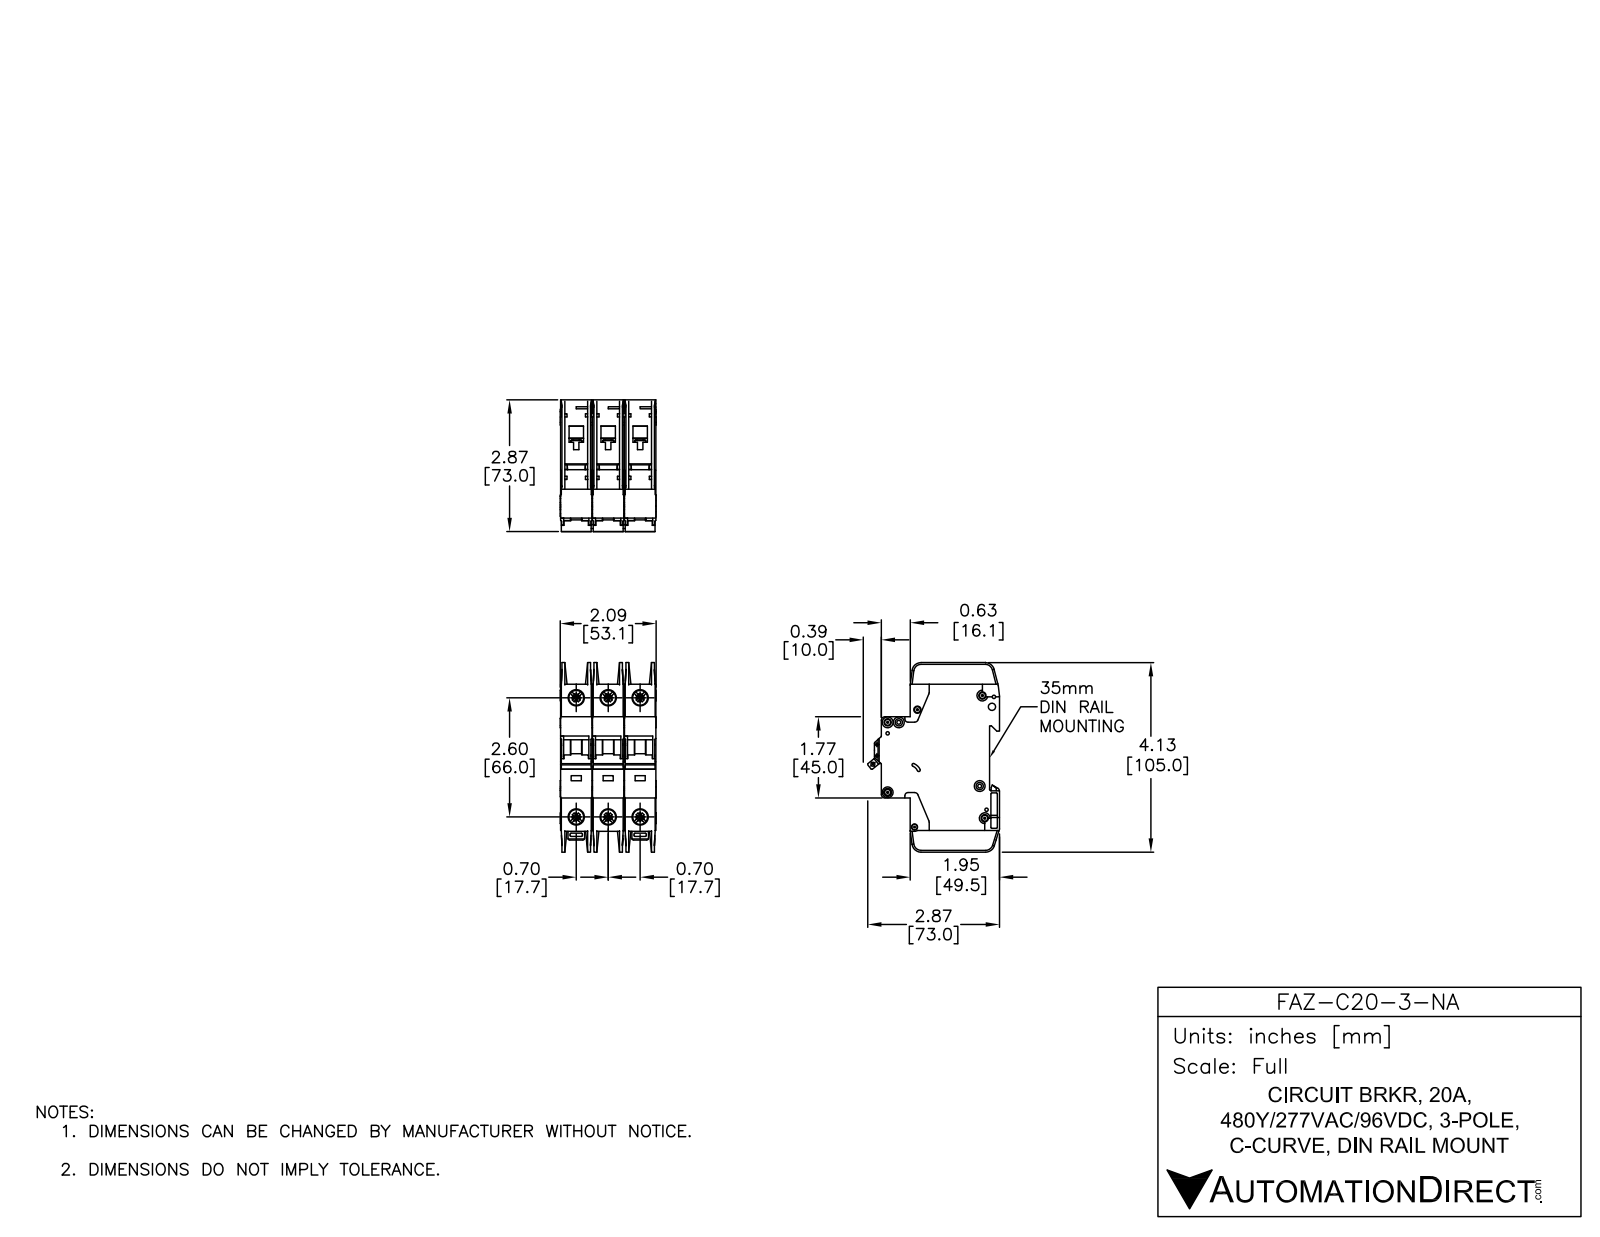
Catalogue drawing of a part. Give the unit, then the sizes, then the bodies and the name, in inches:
Units: inches
Overall size (bounding box): 4.134 × 2.876 × 2.091
Round holes (diameter × count): ⌀0.142 ×7, ⌀0.281 ×6, ⌀0.323 ×6, ⌀0.043 ×2, ⌀0.059 ×2, ⌀0.157 ×2, ⌀0.075 ×1, ⌀0.085 ×1, ⌀0.087 ×1, ⌀0.1 ×1, ⌀0.13 ×1, ⌀0.134 ×1
Round bosses / shafts (diameter × count): ⌀0.236 ×7, ⌀0.098 ×3
Partial cylindrical surfaces — rounded edges, fillets, slot ends (radius × count): R0.01 ×65, R0.02 ×30, R0.039 ×26, R0.079 ×14, R0.071 ×5, R0.197 ×5, R0.157 ×4, R0.008 ×2
Main face-to-face distances: 0.697, 1.394, 0.689, 1.386, 0.028, 0.593, 0.096, 0.069, 0.62, 0.524
Hole centre spacings: 0.697, 2.69, 2.598, 0.244, 1.394, 2.948, 0.204, 0.24
Volume: 14.22 in³ · Surface area: 115 in²
Bodies: 9 solids, 2352 faces (1227 planar, 789 cylindrical, 336 other)
Part name (STEP PRODUCT): FAZ-C20-3-NA
STEP written by: SolidWorks 2014 (AUTOMOTIVE_DESIGN)
